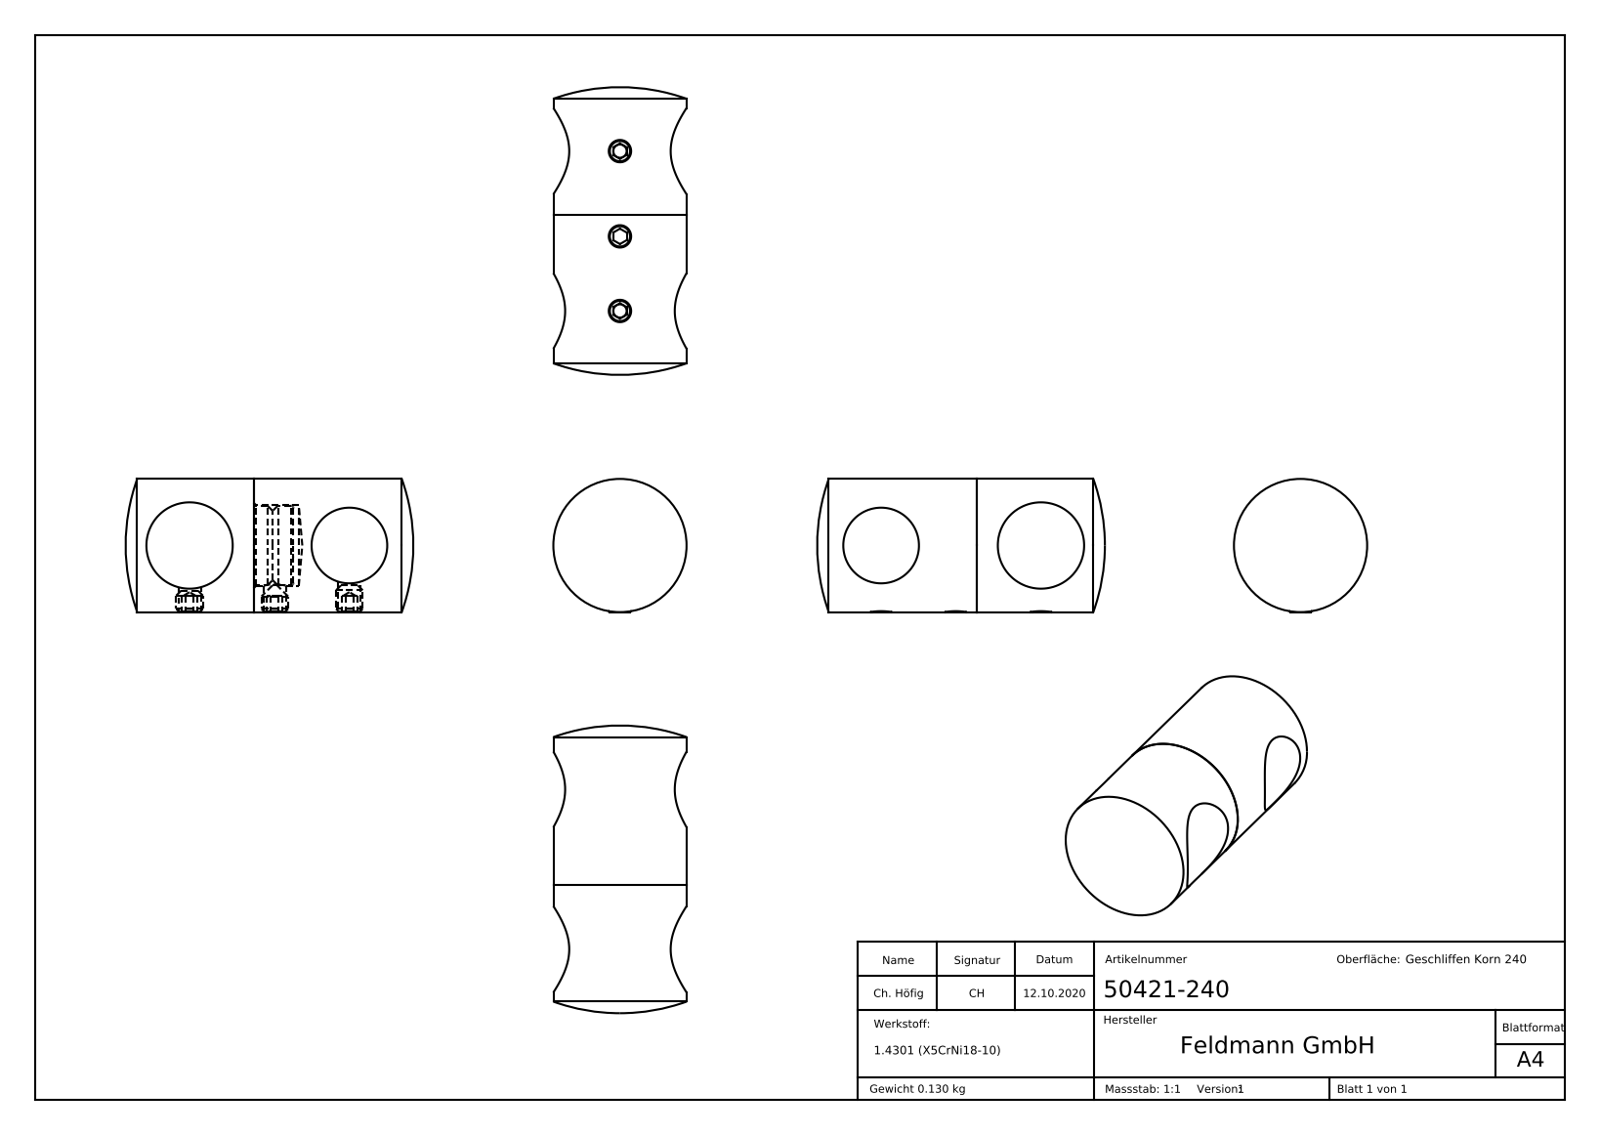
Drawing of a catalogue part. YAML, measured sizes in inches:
part_name: "DIN914; Doppelquerstabhalter Teil1; 50421-240; Doppelquerstabhalter Teil1_50421-240 Teil1 (+6 more)"
step_written_by: "SolidWorks 2018 (CONFIG_CONTROL_DESIGN)"
units: inches
bodies: {solids: 5, faces: 314, planar: 172, cylindrical: 26, other: 116}
overall_size: [2.795, 2.126, 0.984]
volume: 1.005
surface_area: 13.19
round_holes:
  - {diameter: 0.165, count: 3}
  - {diameter: 0.559, count: 1}
  - {diameter: 0.594, count: 1}
  - {diameter: 0.638, count: 1}
round_bosses_or_shafts:
  - {diameter: 0.197, count: 3}
  - {diameter: 0.984, count: 1}
  - {diameter: 0.591, count: 1}
face_to_face_distances: [0.295, 0.098, 1.023, 0.545, 0.478, 0.039, 0.197, 1.121, 0.924, 0.447]
hole_center_spacings: [1.181, 0.551, 0.63]
